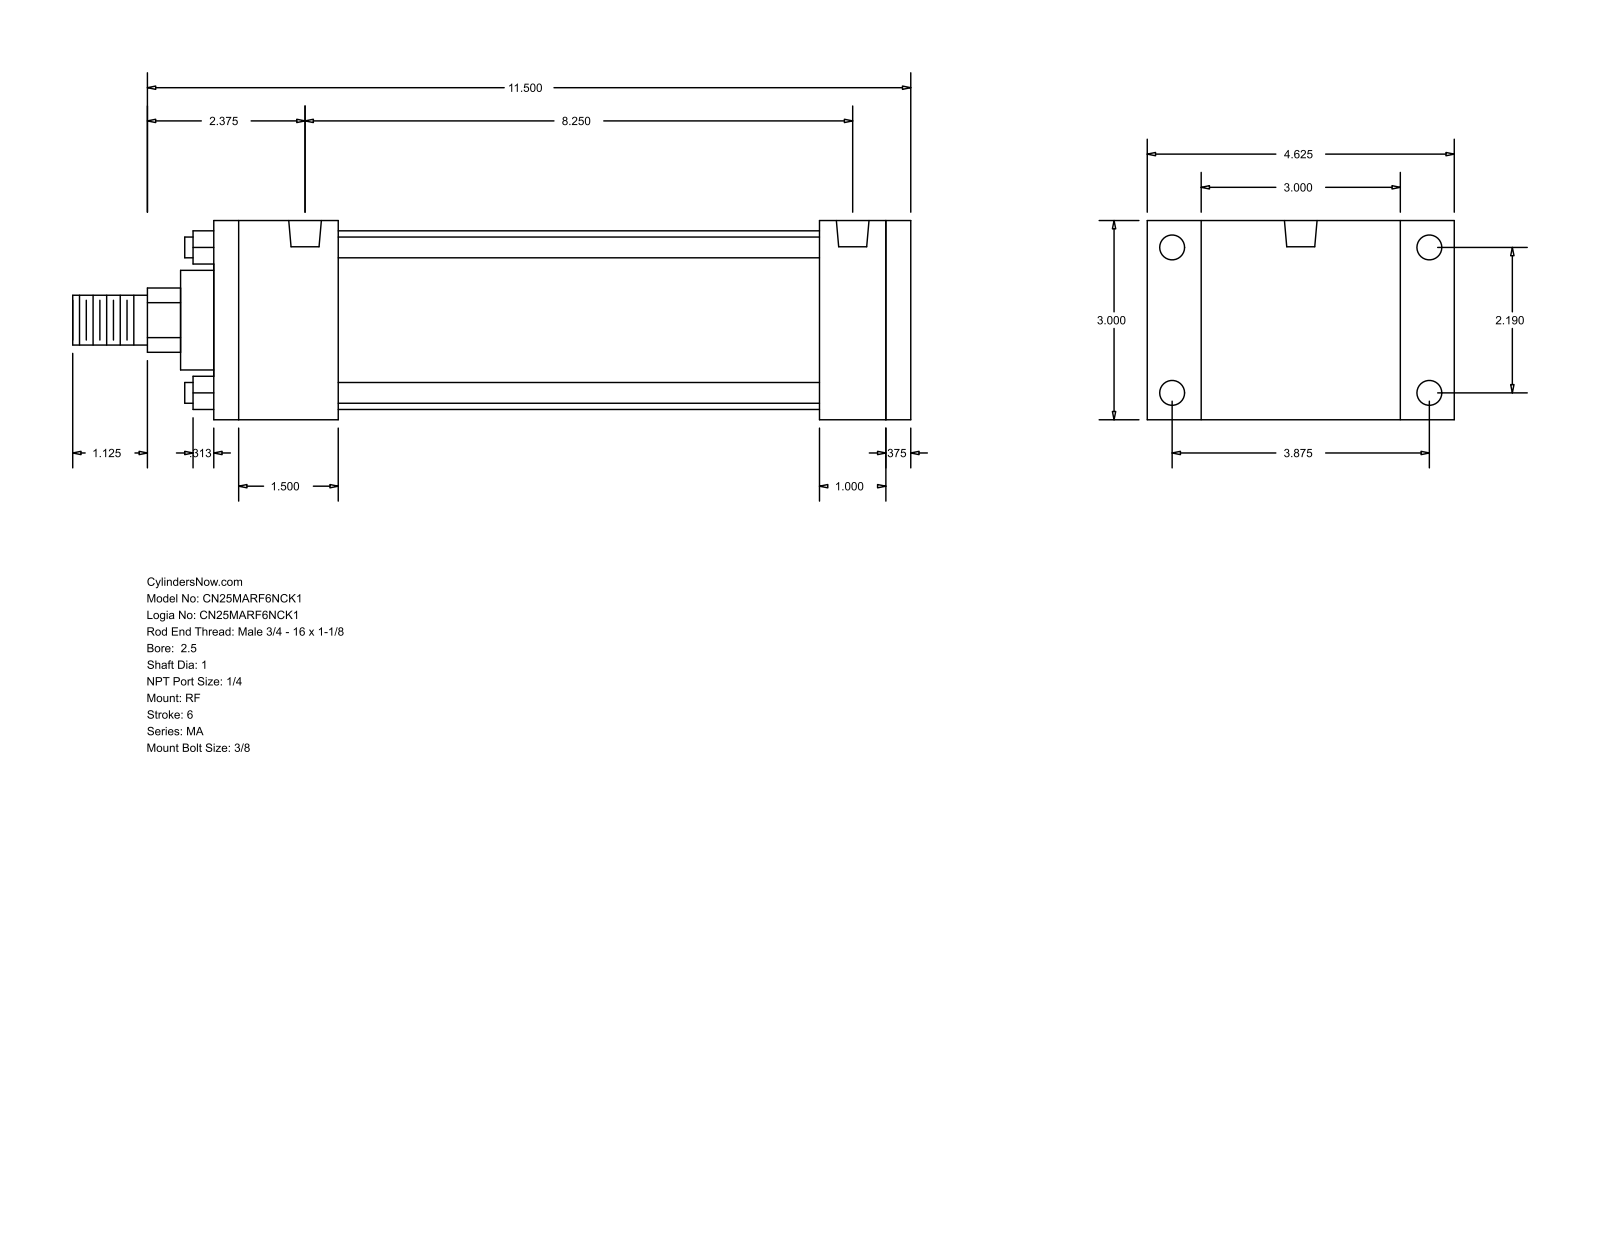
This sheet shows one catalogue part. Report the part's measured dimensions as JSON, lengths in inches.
{"part_name": "MA_RF__0250_1", "step_written_by": "GSSL Pune (CONFIG_CONTROL_DESIGN)", "units": "inches", "bodies": {"solids": 0, "faces": 92, "planar": 64, "cylindrical": 28, "other": 0}, "overall_size": [12.625, 4.625, 3], "round_holes": [[0.313, 4], [0.375, 4], [0.492, 2]], "round_bosses_or_shafts": [[0.313, 4], [2.69, 1], [1.5, 1], [1, 1], [0.75, 1]], "partial_cylinders_radius": [[0.484, 1]], "face_to_face_distances": [3, 10.5, 0.375, 10.125, 1.875, 9.125, 7.25, 8.25, 8.625, 1], "hole_center_spacings": [2.19, 3.875, 4.451, 8.25]}
